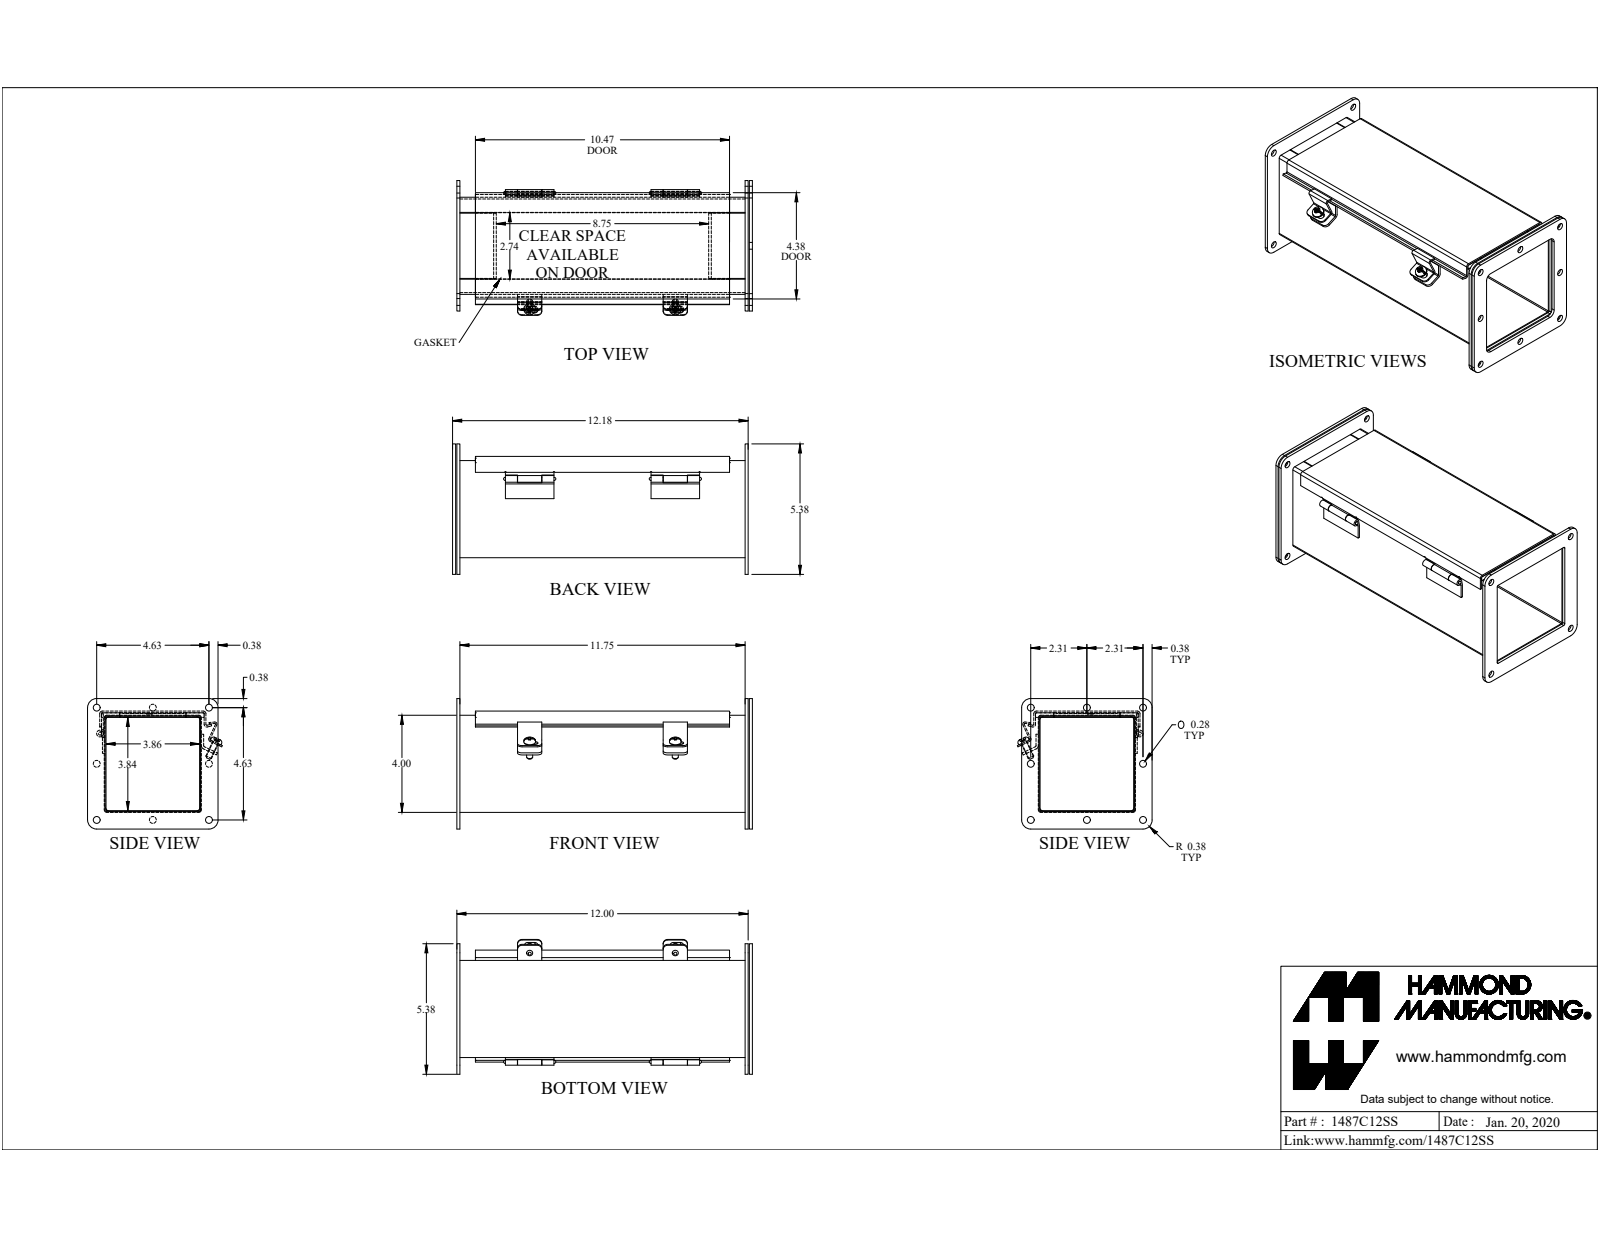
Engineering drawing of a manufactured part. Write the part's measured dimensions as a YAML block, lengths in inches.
part_name: "1487C12SS"
step_written_by: "SolidWorks 2019 (CONFIG_CONTROL_DESIGN)"
units: inches
bodies: {solids: 27, faces: 546, planar: 350, cylindrical: 144, other: 52}
overall_size: [12.561, 5.552, 5.375]
volume: 25.92
surface_area: 646.3
round_holes:
  - {diameter: 0.281, count: 8}
  - {diameter: 0.213, count: 2}
  - {diameter: 0.187, count: 1}
  - {diameter: 0.196, count: 1}
  - {diameter: 0.258, count: 1}
  - {diameter: 0.35, count: 1}
round_bosses_or_shafts:
  - {diameter: 0.25, count: 3}
  - {diameter: 0.48, count: 2}
  - {diameter: 0.5, count: 1}
  - {diameter: 0.337, count: 1}
  - {diameter: 0.18, count: 1}
partial_cylinders:
  - {radius: 0.188, count: 8}
  - {radius: 0.375, count: 8}
  - {radius: 0.036, count: 7}
  - {radius: 0.108, count: 7}
  - {radius: 0.02, count: 6}
  - {radius: 0.03, count: 4}
  - {radius: 0.062, count: 4}
  - {radius: 0.141, count: 4}
face_to_face_distances: [0.072, 3.928, 4.1, 4, 3.856, 4.028, 4.172, 0.172, 0.187, 0.259]
hole_center_spacings: [2.313, 5.171, 4.625, 4.625, 2.312, 3.27, 3.27, 5.171]
